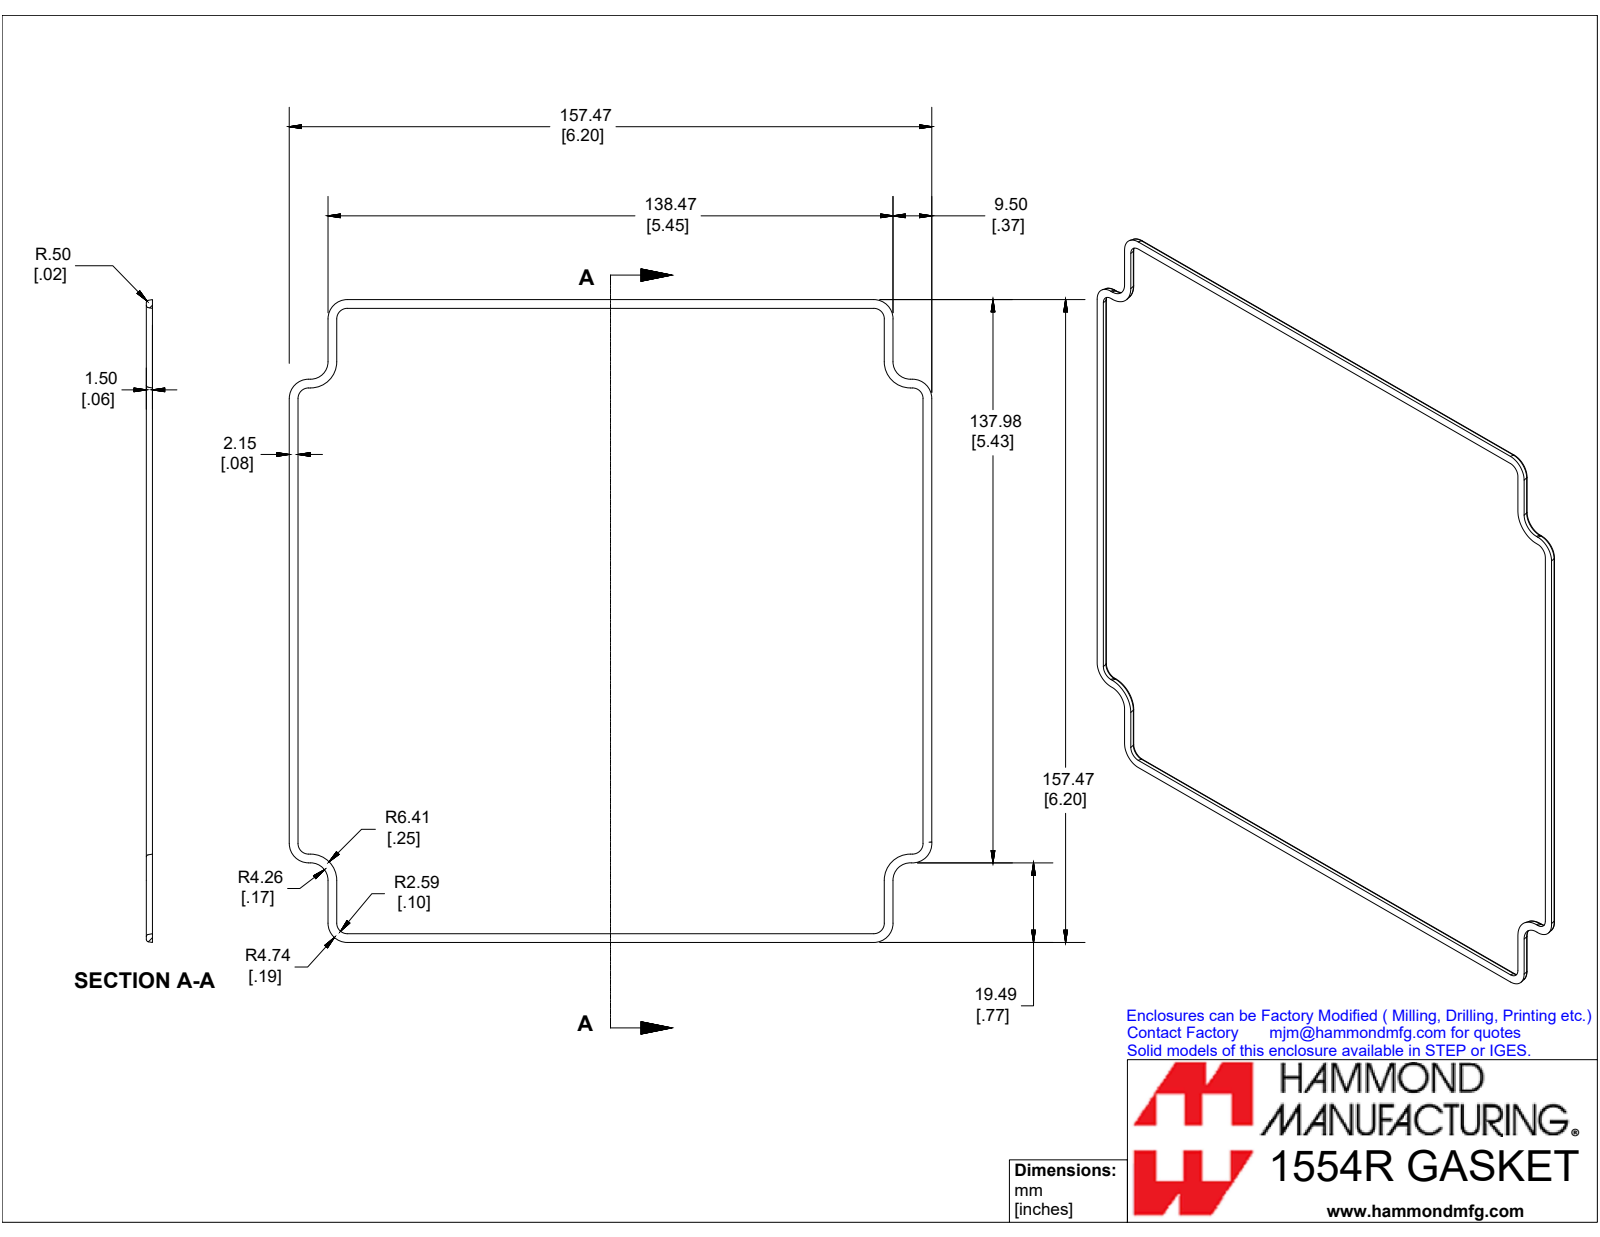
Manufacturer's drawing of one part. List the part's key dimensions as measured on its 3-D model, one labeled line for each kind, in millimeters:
Part name (STEP PRODUCT): 1554RGASKET
STEP written by: SolidWorks 2019 (CONFIG_CONTROL_DESIGN)
Units: millimetres
Bodies: 1 solid, 96 faces (25 planar, 23 cylindrical, 48 other)
Overall size (bounding box): 157.5 × 157.5 × 1.5
Volume: 1 660 mm³ · Surface area: 3 917 mm²
Partial cylindrical surfaces — rounded edges, fillets, slot ends (radius × count): R0.5 ×16
Main face-to-face distances: 1.5, 153, 153, 143.6, 9.4, 9.3, 143.6, 134.3, 134.3, 19.2
